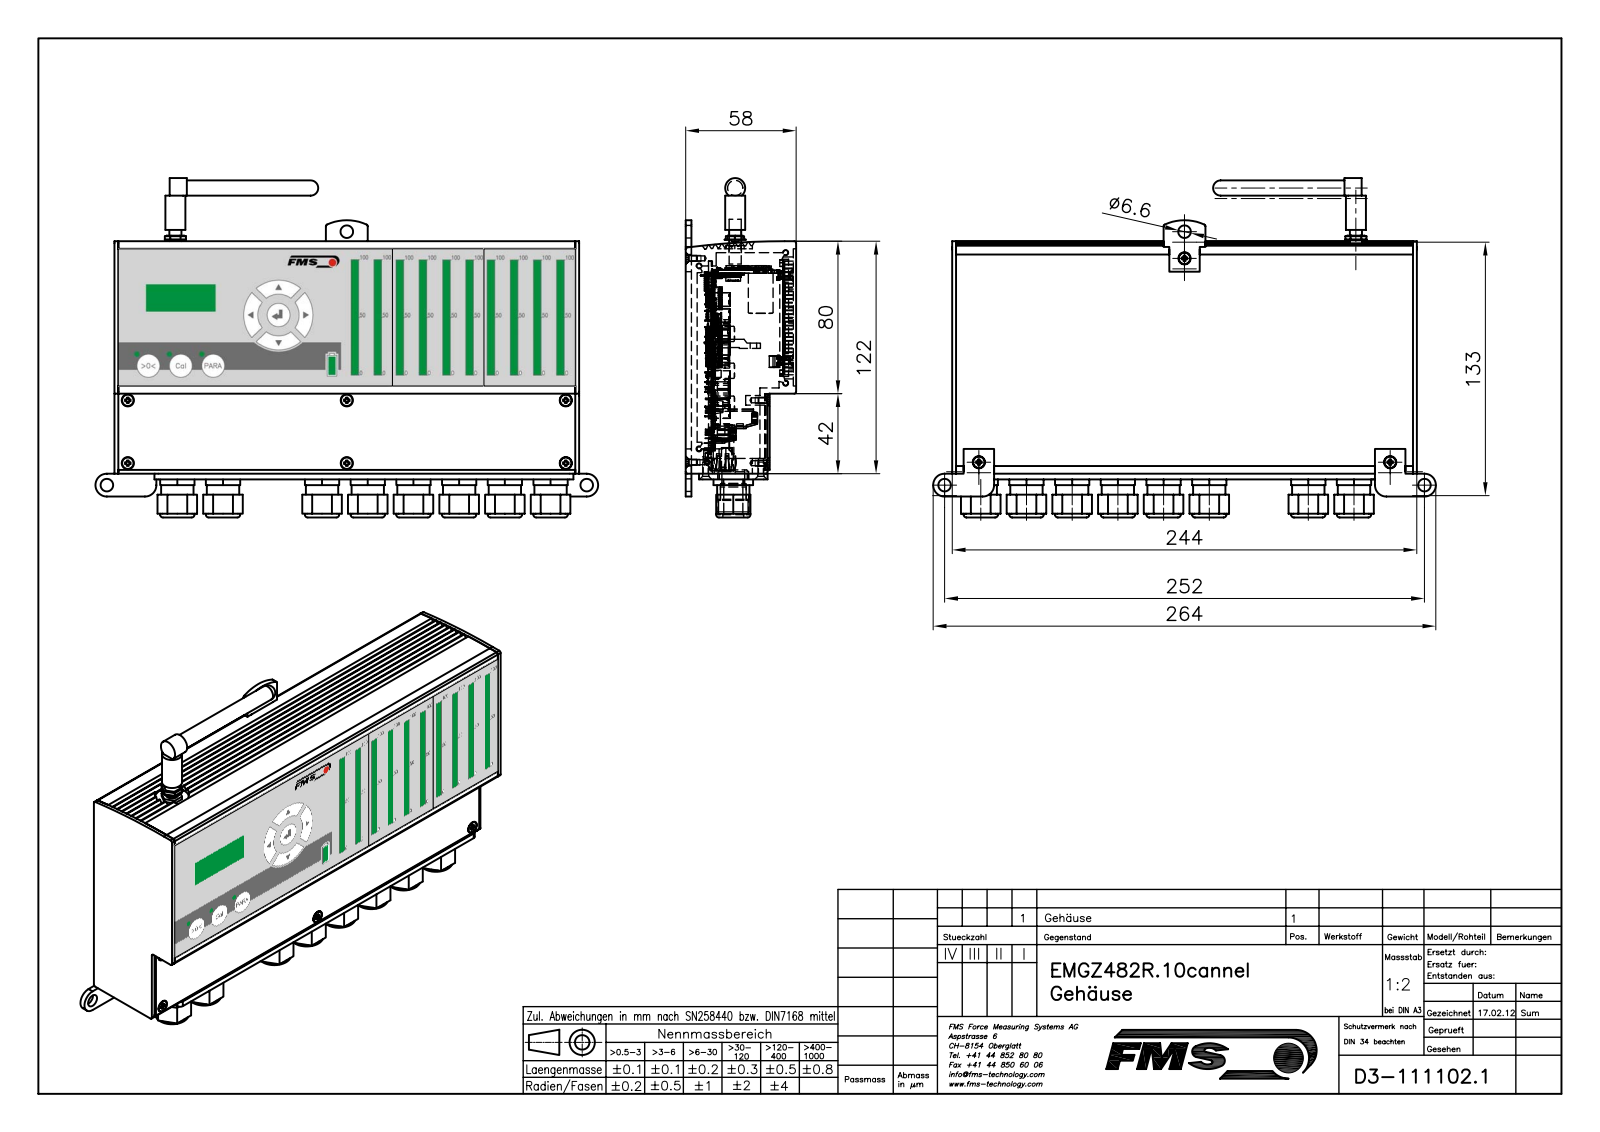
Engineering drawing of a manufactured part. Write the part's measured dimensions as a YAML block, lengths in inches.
part_name: "T1111021; T1111022; E0708103; T1111023 (+8 more)"
step_written_by: "Mechanical Desktop 2009 (CONFIG_CONTROL_DESIGN)"
units: inches
bodies: {solids: 7549, faces: 90065, planar: 47031, cylindrical: 7713, other: 35321}
overall_size: [10.394, 7.014, 2.287]
volume: 31.53
surface_area: 732.5
round_holes:
  - {diameter: 0.035, count: 64}
  - {diameter: 0.039, count: 62}
  - {diameter: 0.051, count: 40}
  - {diameter: 0.118, count: 40}
  - {diameter: 0.024, count: 24}
  - {diameter: 0.126, count: 21}
  - {diameter: 0.102, count: 20}
  - {diameter: 0.067, count: 12}
  - {diameter: 0.165, count: 12}
  - {diameter: 0.009, count: 10}
  - {diameter: 0.031, count: 10}
  - {diameter: 0.079, count: 10}
round_bosses_or_shafts:
  - {diameter: 0.118, count: 22}
  - {diameter: 0.236, count: 21}
  - {diameter: 0.219, count: 12}
  - {diameter: 0.207, count: 12}
  - {diameter: 0.165, count: 12}
  - {diameter: 0.153, count: 12}
  - {diameter: 0.141, count: 12}
  - {diameter: 0.047, count: 6}
partial_cylinders:
  - {radius: 0.004, count: 824}
  - {radius: 0.008, count: 106}
  - {radius: 0.006, count: 57}
  - {radius: 0.012, count: 28}
  - {radius: 0.079, count: 24}
  - {radius: 0.005, count: 10}
  - {radius: 0.039, count: 8}
  - {radius: 0.004, count: 4}
face_to_face_distances: [0.118, 0.079, 1.89, 0.236, 1.421, 1.539, 2.008, 1.654, 0.098, 0.354]
hole_center_spacings: [0.1, 0.945, 2.008, 1.89, 2.591, 1.772, 2.835, 3.343]
